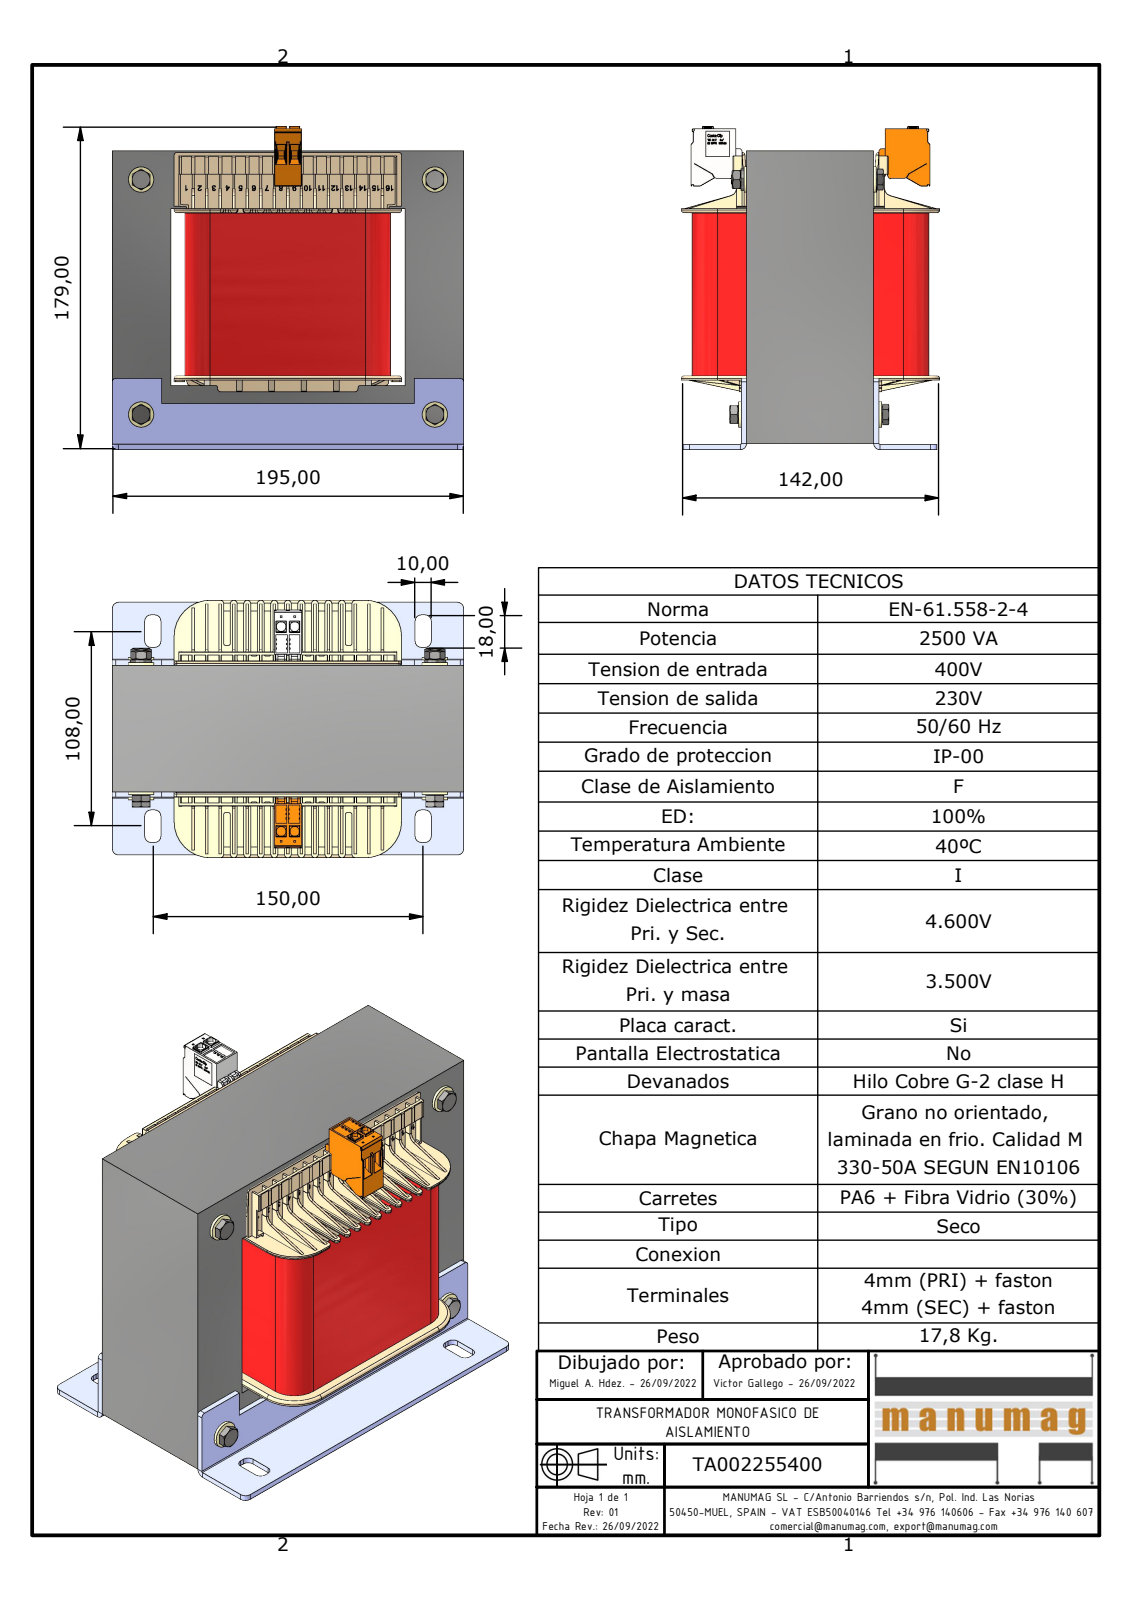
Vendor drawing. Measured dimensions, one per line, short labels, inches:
name: TA002255400; EI195 x 162 - 70 (Rc65); EI192_70_AK_25379_8_Wz837 Con bobinado; 195 (+6 more)
written by: Autodesk Inventor 2023 (AUTOMOTIVE_DESIGN)
unit: in
bodies: 24 solids, 5945 faces (3974 planar, 698 cylindrical, 1273 other)
size: 7.677 × 7.047 × 5.614
volume: 121.9 in³; area: 625.6 in²
holes: 4× ⌀0.194, 4× ⌀0.236, 4× ⌀0.433, 2× ⌀0.252, 2× ⌀0.39
bosses: 4× ⌀0.551, 4× ⌀0.343, 4× ⌀0.299, 4× ⌀0.215, 2× ⌀0.472
rounds: 146× R0.006, 64× R0.008, 52× R0.039, 44× R0.059, 28× R0.02, 22× R0.077, 22× R0.138, 12× R0.012
face distances: 5.118, 0.118, 1.28, 2.756, 6.398, 2.874, 2.559, 1.26, 3.646, 0.094
hole spacings: 5.118, 6.417, 8.208
